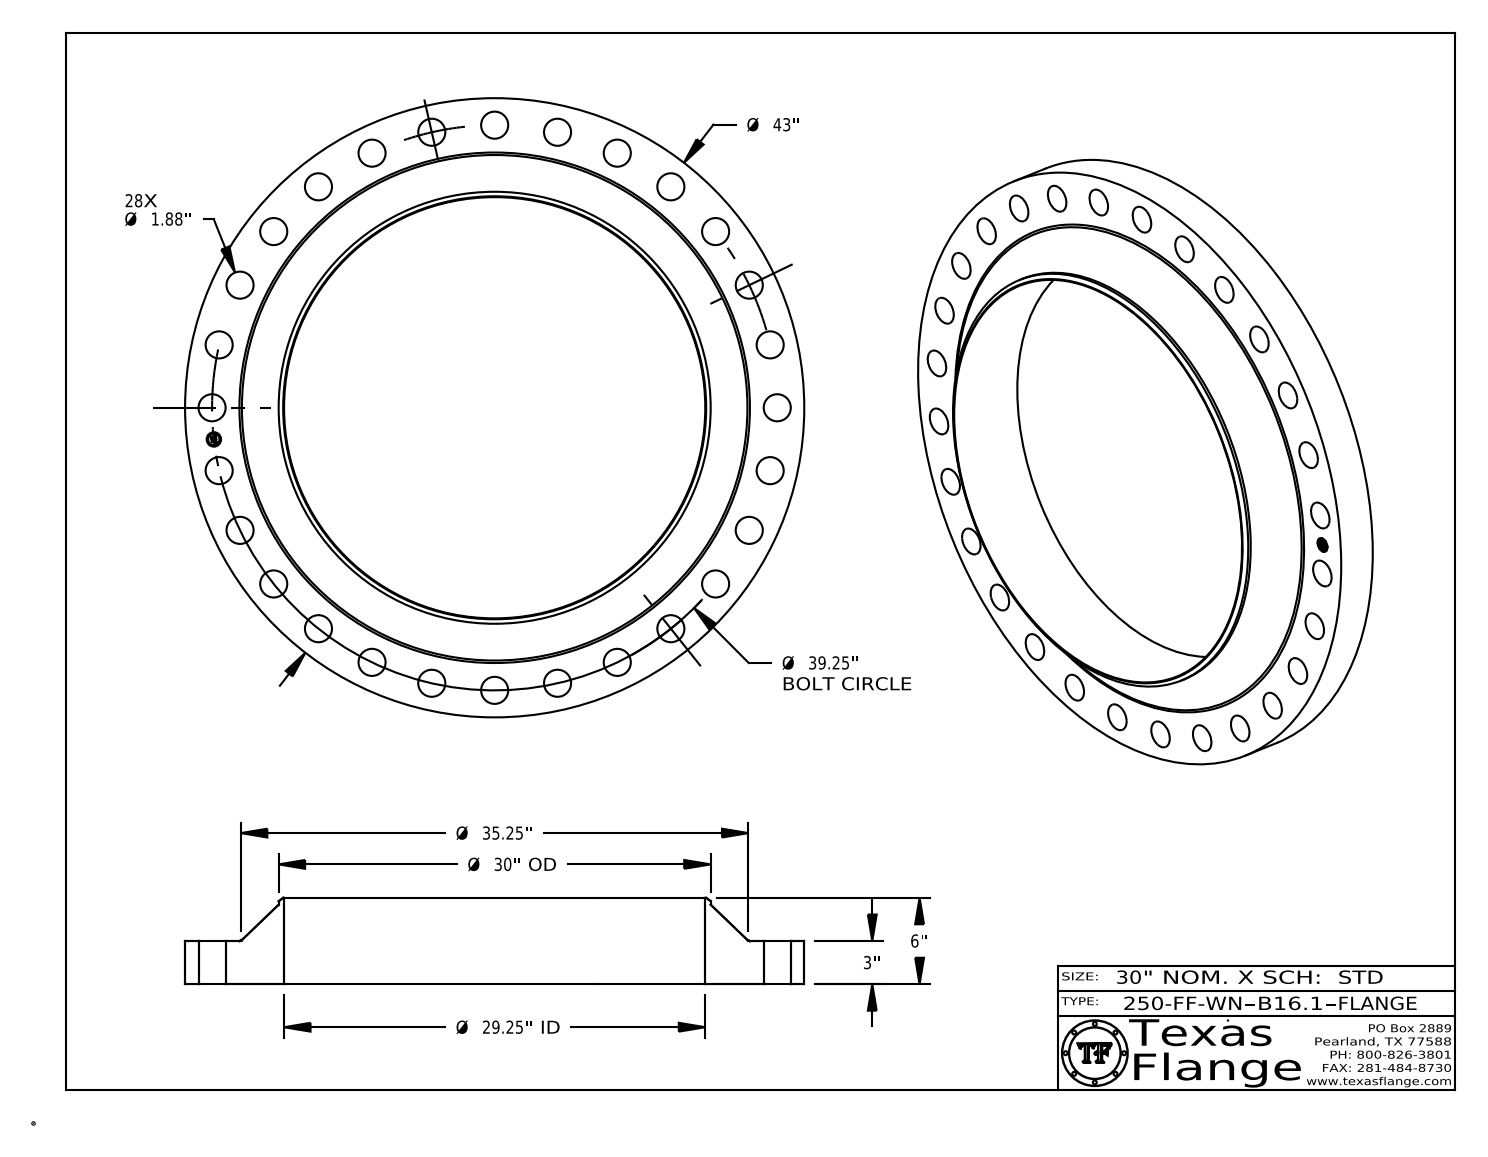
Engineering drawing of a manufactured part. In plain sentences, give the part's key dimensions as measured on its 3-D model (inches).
The part is named "250-FF-WN, B16.1". Its 3-D file was written by "CATIA V5 STEP AP214 (AUTOMOTIVE_DESIGN)". It is 1 solid with 456 faces: 368 planar, 82 cylindrical and 6 other. Overall it measures 43 by 43 by 6 inches. Its volume is 2 539 cubic inches and its surface area 2 991 square inches. Round holes: 28 of diameter 1.88, 1 of diameter 1, 1 of diameter 29.25. Round bosses or shafts: 8 of diameter 0.061, 1 of diameter 43, 1 of diameter 30, 1 of diameter 0.788. The main face-to-face distances are 3, 6, 2.985, 0.015, 3.015, 0.298, 0.293, 0.054, 0.193, 0.248. The hole center spacings are 4.394, 8.734, 12.963, 17.03, 20.882, 35.363, 24.472, 33.234.
